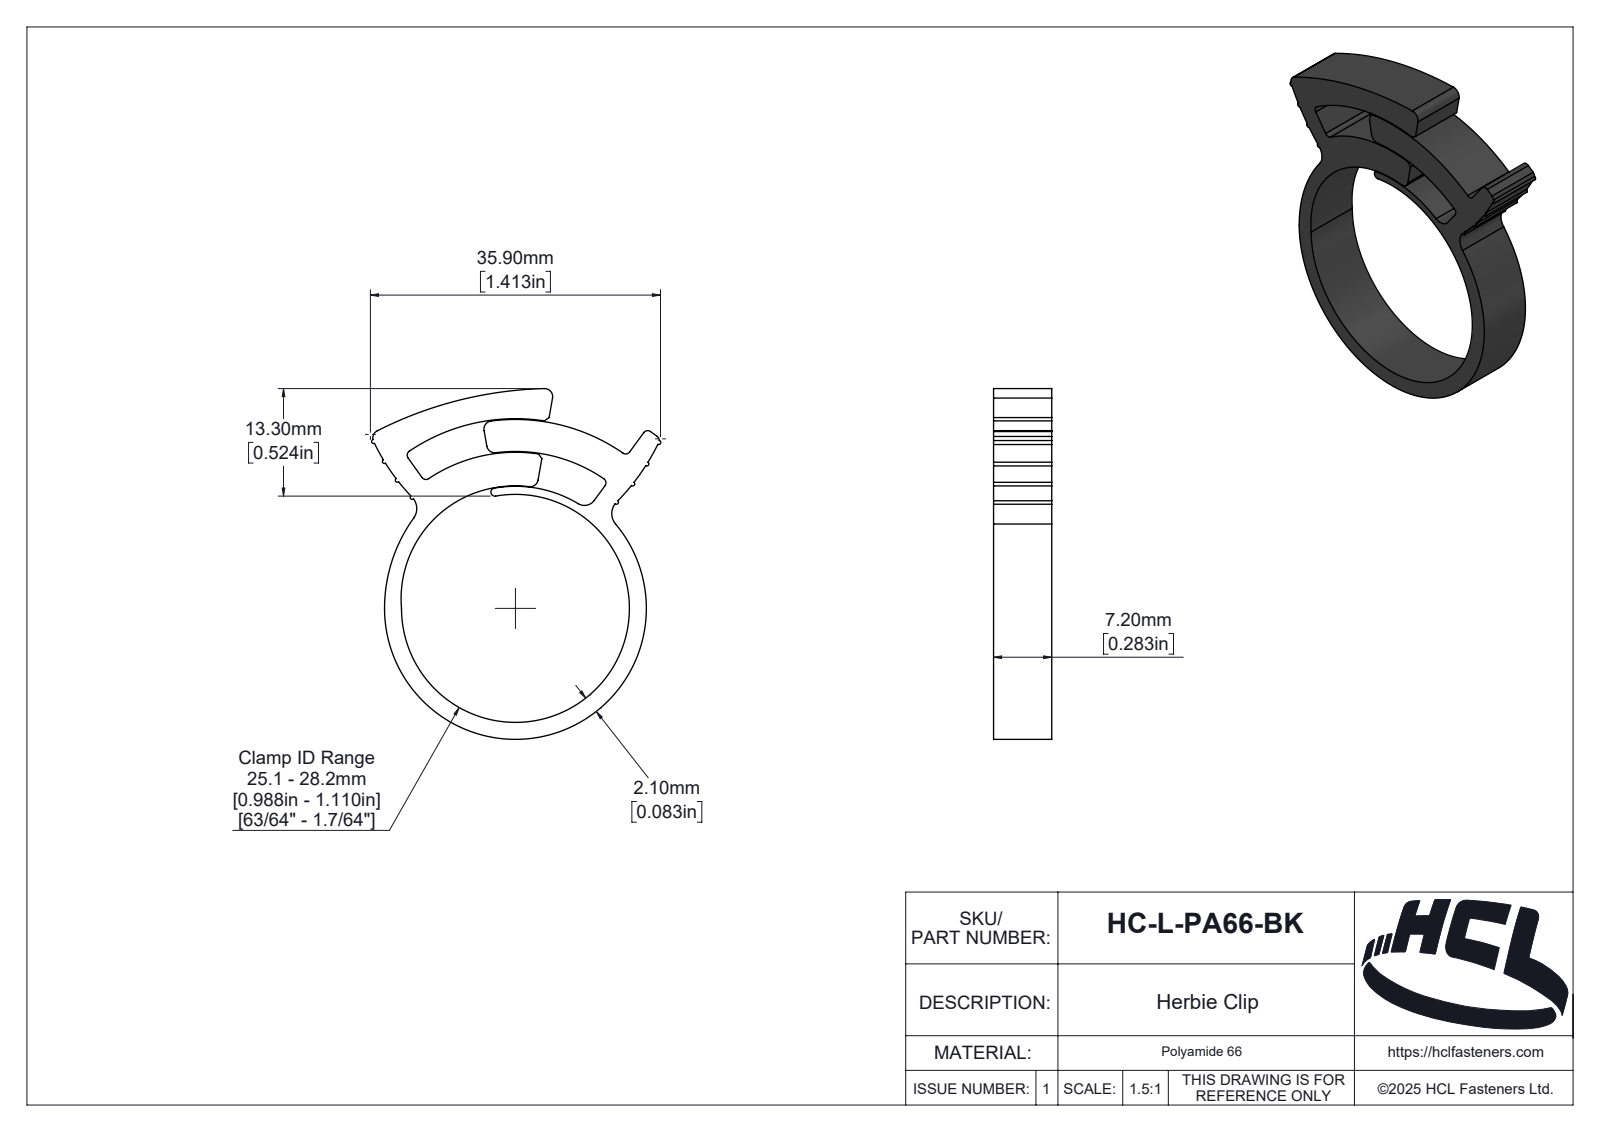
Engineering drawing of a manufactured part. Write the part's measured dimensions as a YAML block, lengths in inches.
part_name: "HC-L-PA66-BK"
step_written_by: "SolidWorks 2025 (AUTOMOTIVE_DESIGN)"
units: inches
bodies: {solids: 1, faces: 162, planar: 13, cylindrical: 100, other: 49}
overall_size: [1.708, 1.409, 0.283]
volume: 0.186
surface_area: 4.934
partial_cylinders:
  - {radius: 0.01, count: 8}
  - {radius: 0.024, count: 6}
  - {radius: 0.039, count: 5}
  - {radius: 0.079, count: 2}
  - {radius: 0.007, count: 1}
  - {radius: 0.02, count: 1}
  - {radius: 0.026, count: 1}
  - {radius: 0.033, count: 1}
face_to_face_distances: [0.283]
